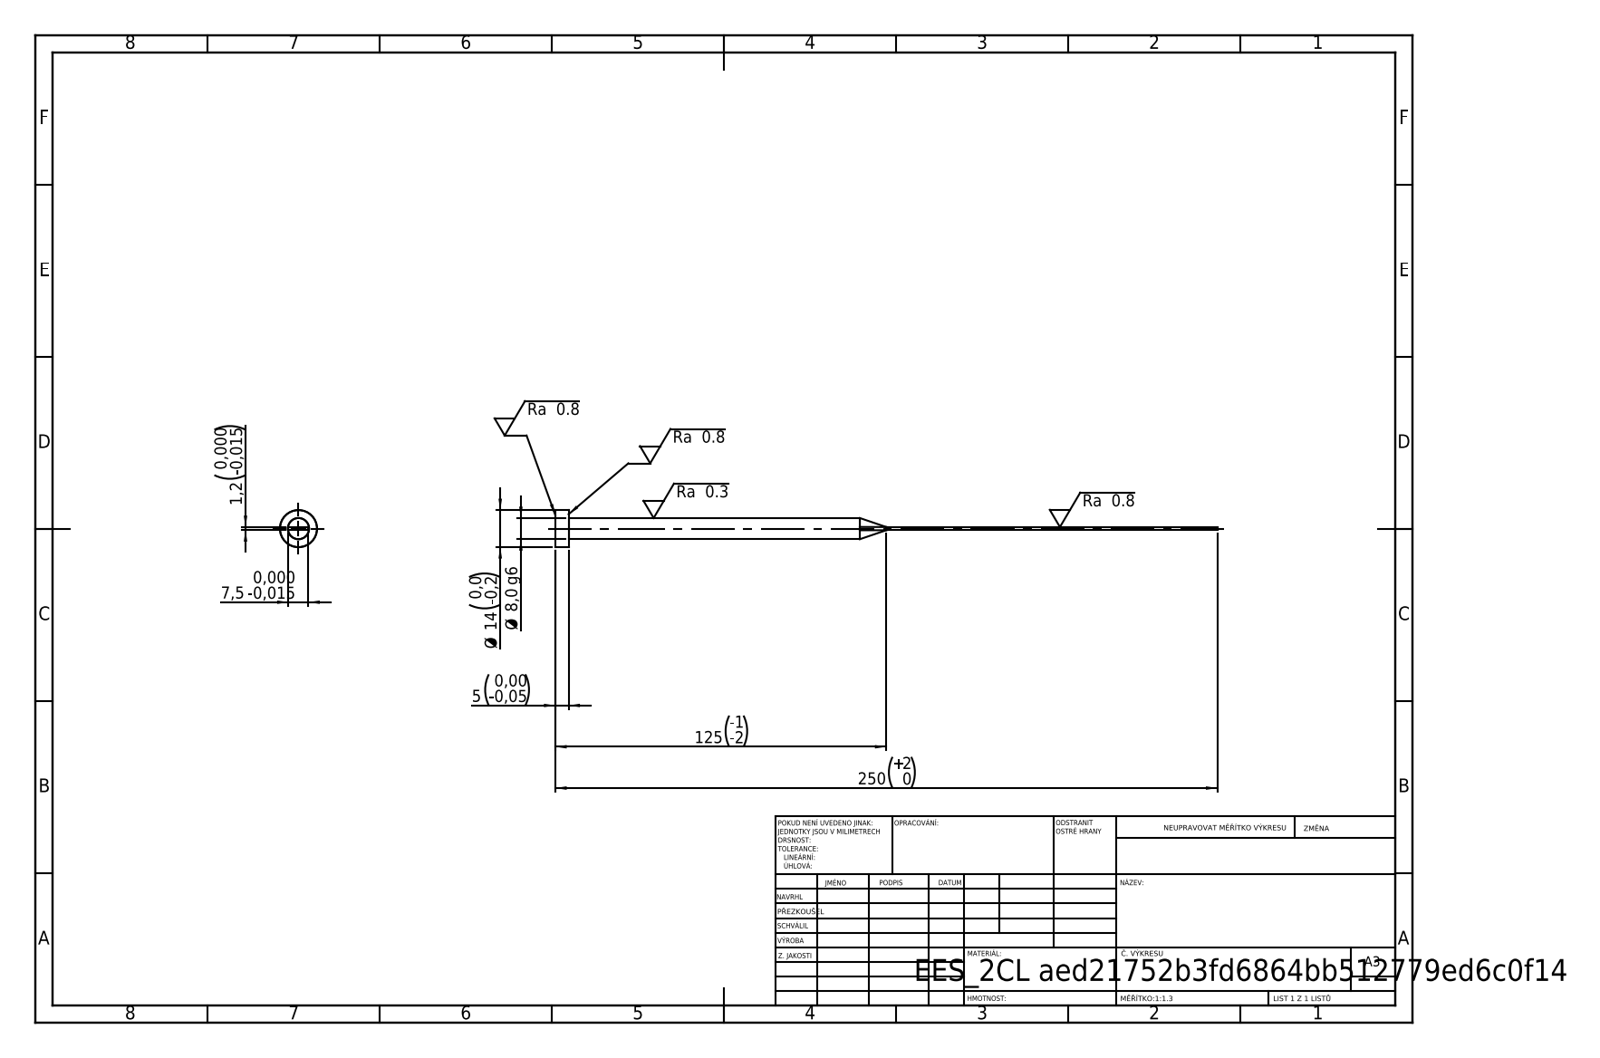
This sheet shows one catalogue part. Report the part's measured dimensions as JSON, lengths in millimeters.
{"step_written_by": "SolidWorks 2019 (CONFIG_CONTROL_DESIGN)", "units": "millimeters", "bodies": {"solids": 1, "faces": 15, "planar": 7, "cylindrical": 4, "other": 4}, "overall_size": [250, 14, 14], "volume_mm3": 7703, "surface_area_mm2": 5634, "round_bosses_or_shafts": [[14, 1], [8, 1]], "face_to_face_distances": [1.2, 7.5, 5, 250, 245]}
